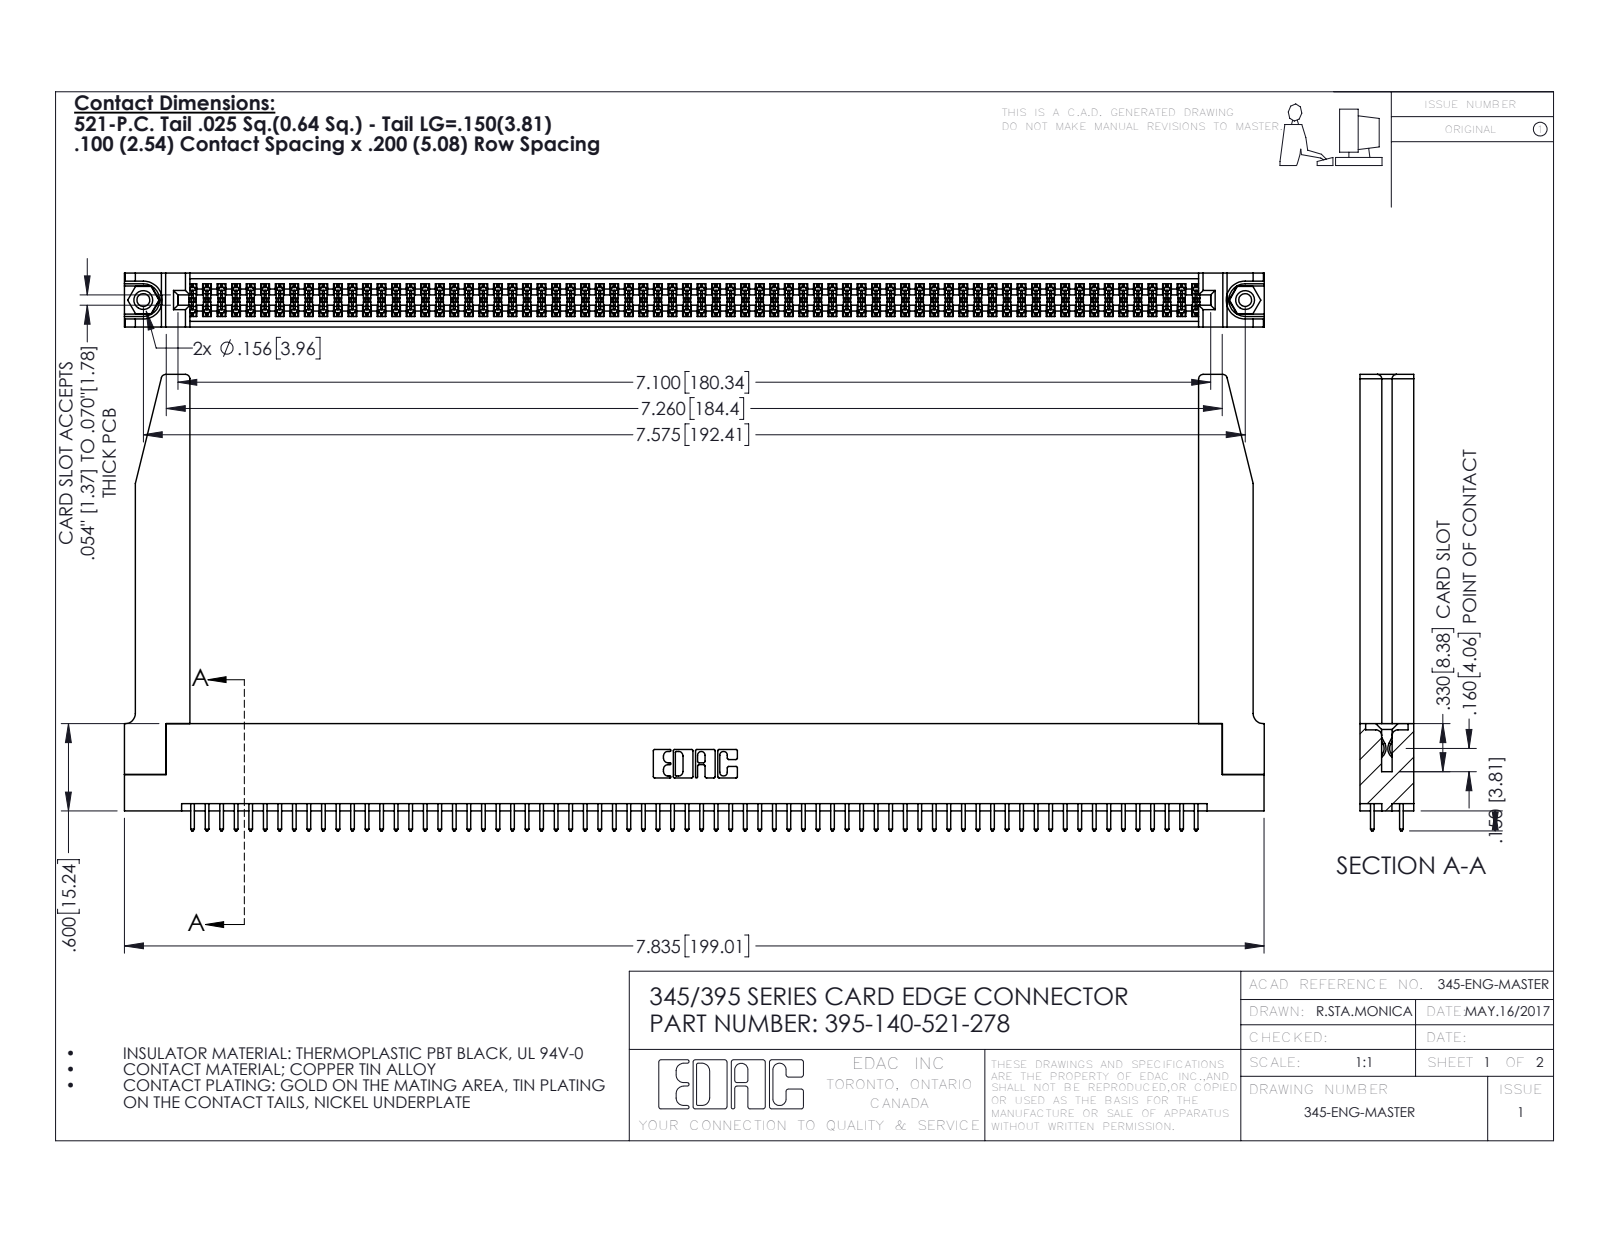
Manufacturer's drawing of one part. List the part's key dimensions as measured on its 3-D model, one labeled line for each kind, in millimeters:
Part name (STEP PRODUCT): 345 Part_Flush Mounting Lugs - 0.156 Dia-TH; 395-140-521-278; 345-250-001_345-250-001-102; 345-220-078_345-220-078 (+1 more)
STEP written by: SolidWorks 2016 (CONFIG_CONTROL_DESIGN)
Units: millimetres
Bodies: 145 solids, 7360 faces (4842 planar, 2466 cylindrical, 52 other)
Overall size (bounding box): 199 × 79.7 × 9.4
Volume: 27 300 mm³ · Surface area: 35 890 mm²
Round holes (diameter × count): ⌀2.3 ×2, ⌀3.2 ×2, ⌀4 ×2, ⌀1.6 ×1
Round bosses / shafts (diameter × count): ⌀3.9 ×2
Partial cylindrical surfaces — rounded edges, fillets, slot ends (radius × count): R0.2 ×210, R0.3 ×140, R0.3 ×22, R0.8 ×8, R0.2 ×6, R0.8 ×6, R0.7 ×3, R0.4 ×2
Main face-to-face distances: 1.8, 7.6, 9.4, 5.1, 2.5, 6.9, 0.6, 5.7, 4.4, 3.8
Hole centre spacings: 6.9, 186.4, 192.4
